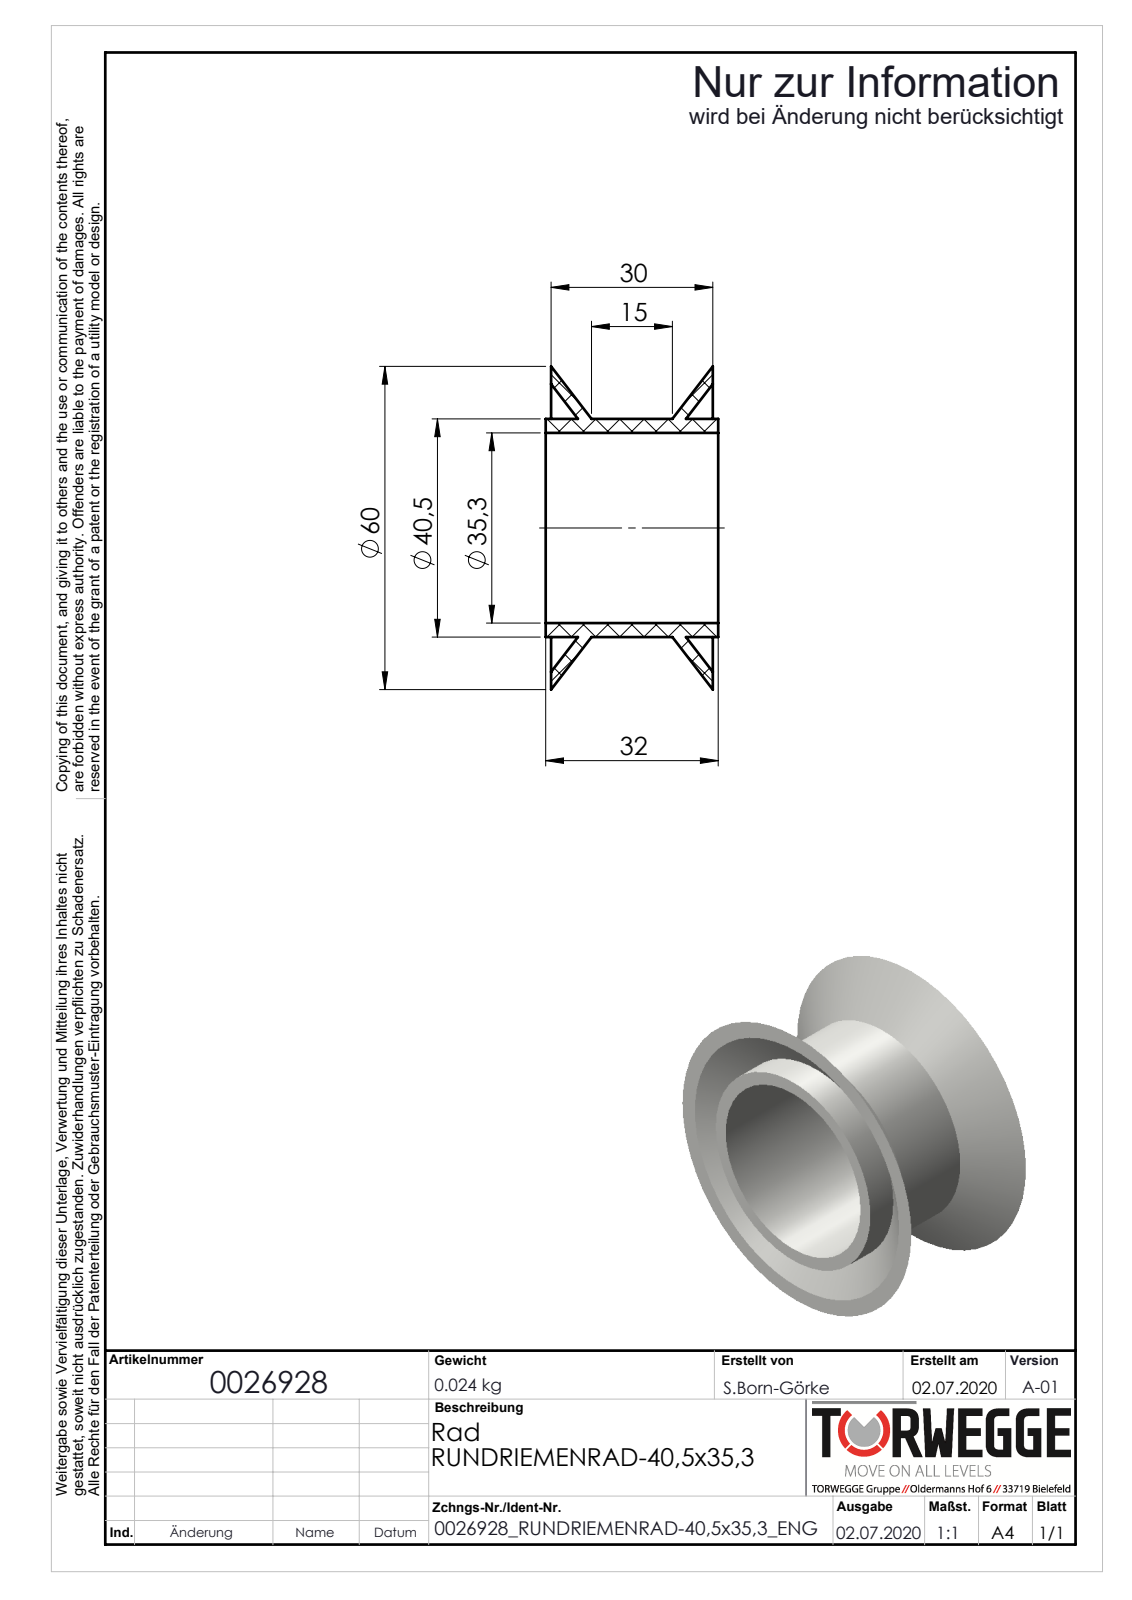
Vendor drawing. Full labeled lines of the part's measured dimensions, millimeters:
Part name (STEP PRODUCT): 0026928
STEP written by: SolidWorks 2018 (AUTOMOTIVE_DESIGN)
Units: millimetres
Bodies: 1 solid, 20 faces (4 planar, 8 cylindrical, 8 other)
Overall size (bounding box): 60 × 60 × 32
Volume: 16 171 mm³ · Surface area: 15 059 mm²
Round holes (diameter × count): ⌀35.3 ×1
Round bosses / shafts (diameter × count): ⌀40.5 ×1
Main face-to-face distances: 1, 31, 30, 32
